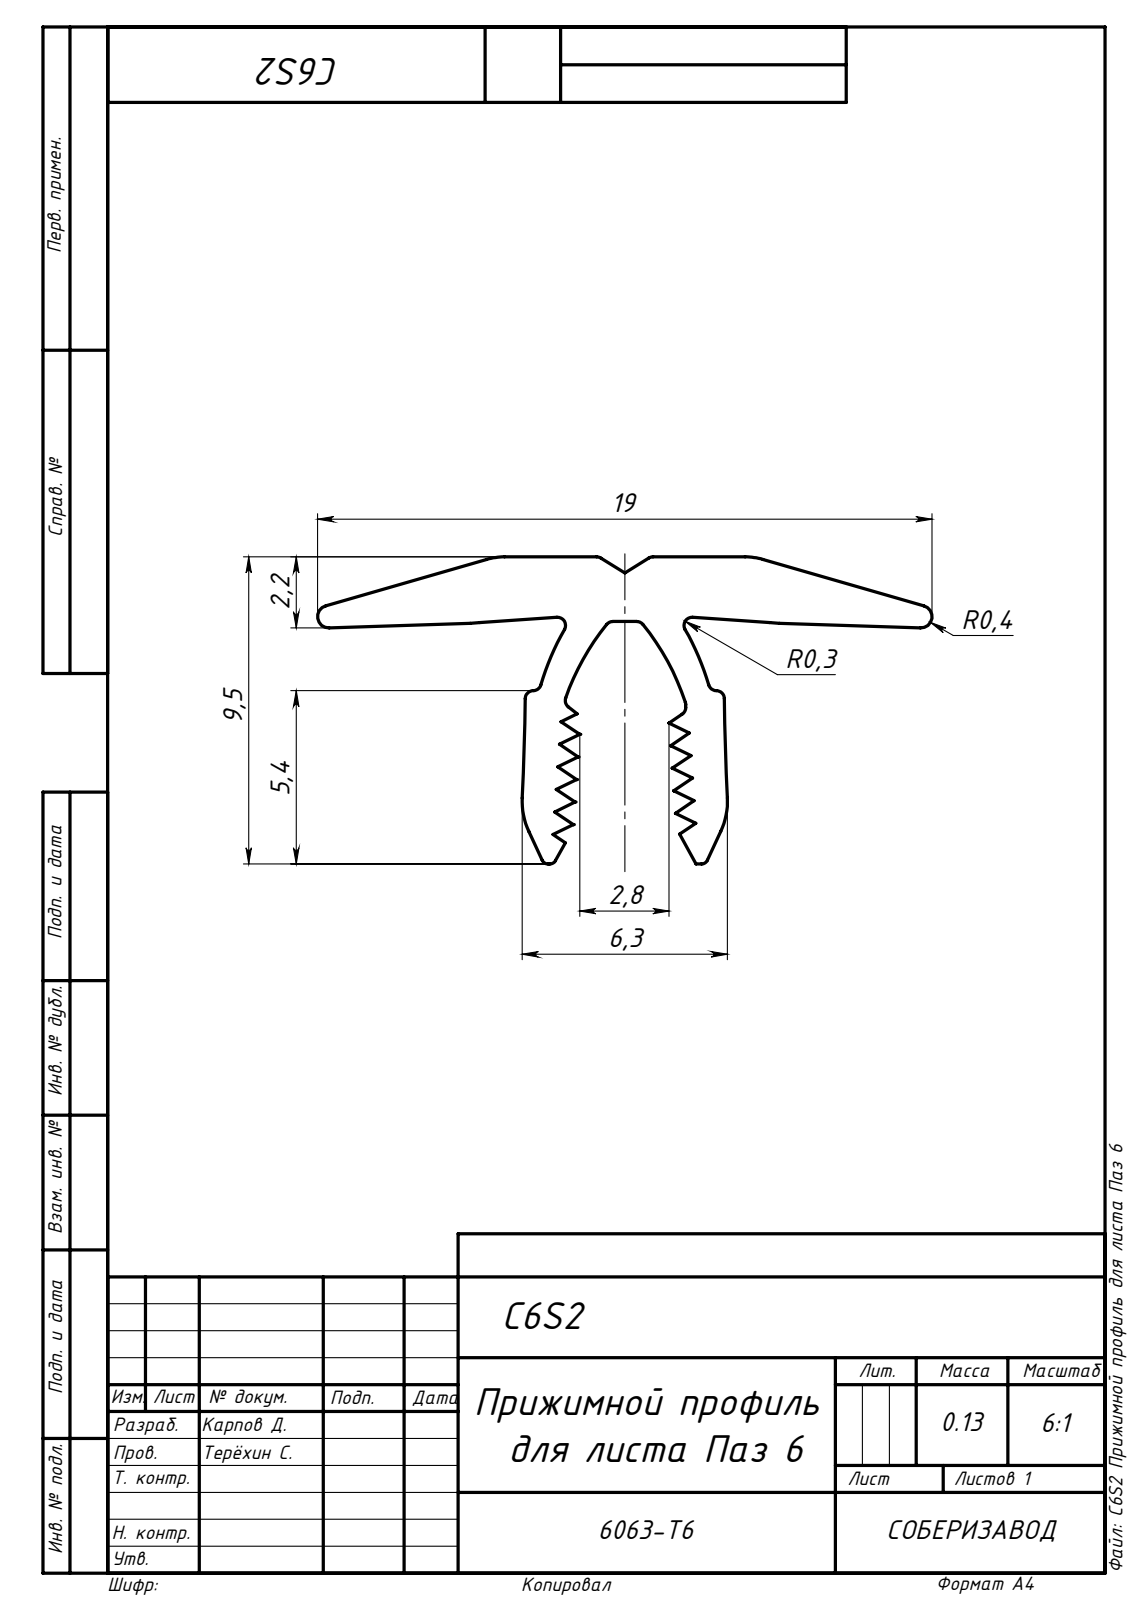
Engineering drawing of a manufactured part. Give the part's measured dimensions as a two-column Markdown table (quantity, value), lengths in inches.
| quantity | value |
| --- | --- |
| part name | C6S2 Прижимной профиль для листа Паз 6 |
| STEP written by | SolidWorks 2018 (AUTOMOTIVE_DESIGN) |
| units | inches |
| bodies | 1 solid, 95 faces (63 planar, 32 cylindrical, 0 other) |
| overall size | 39.371 × 0.748 × 0.374 |
| volume | 2.894 in³ |
| surface area | 120.1 in² |
| partial cylindrical surfaces (radius × count) | 0.01 × 13, 0.008 × 3, 0.014 × 2, 0.079 × 2, 0.087 × 2, 0.157 × 2, 0.3 × 2, 0.324 × 2 |
| main face-to-face distances | 0.048, 0.024, 0.024, 0.072, 0.095, 0.071, 0.119, 0.048, 0.096, 0.079 |
